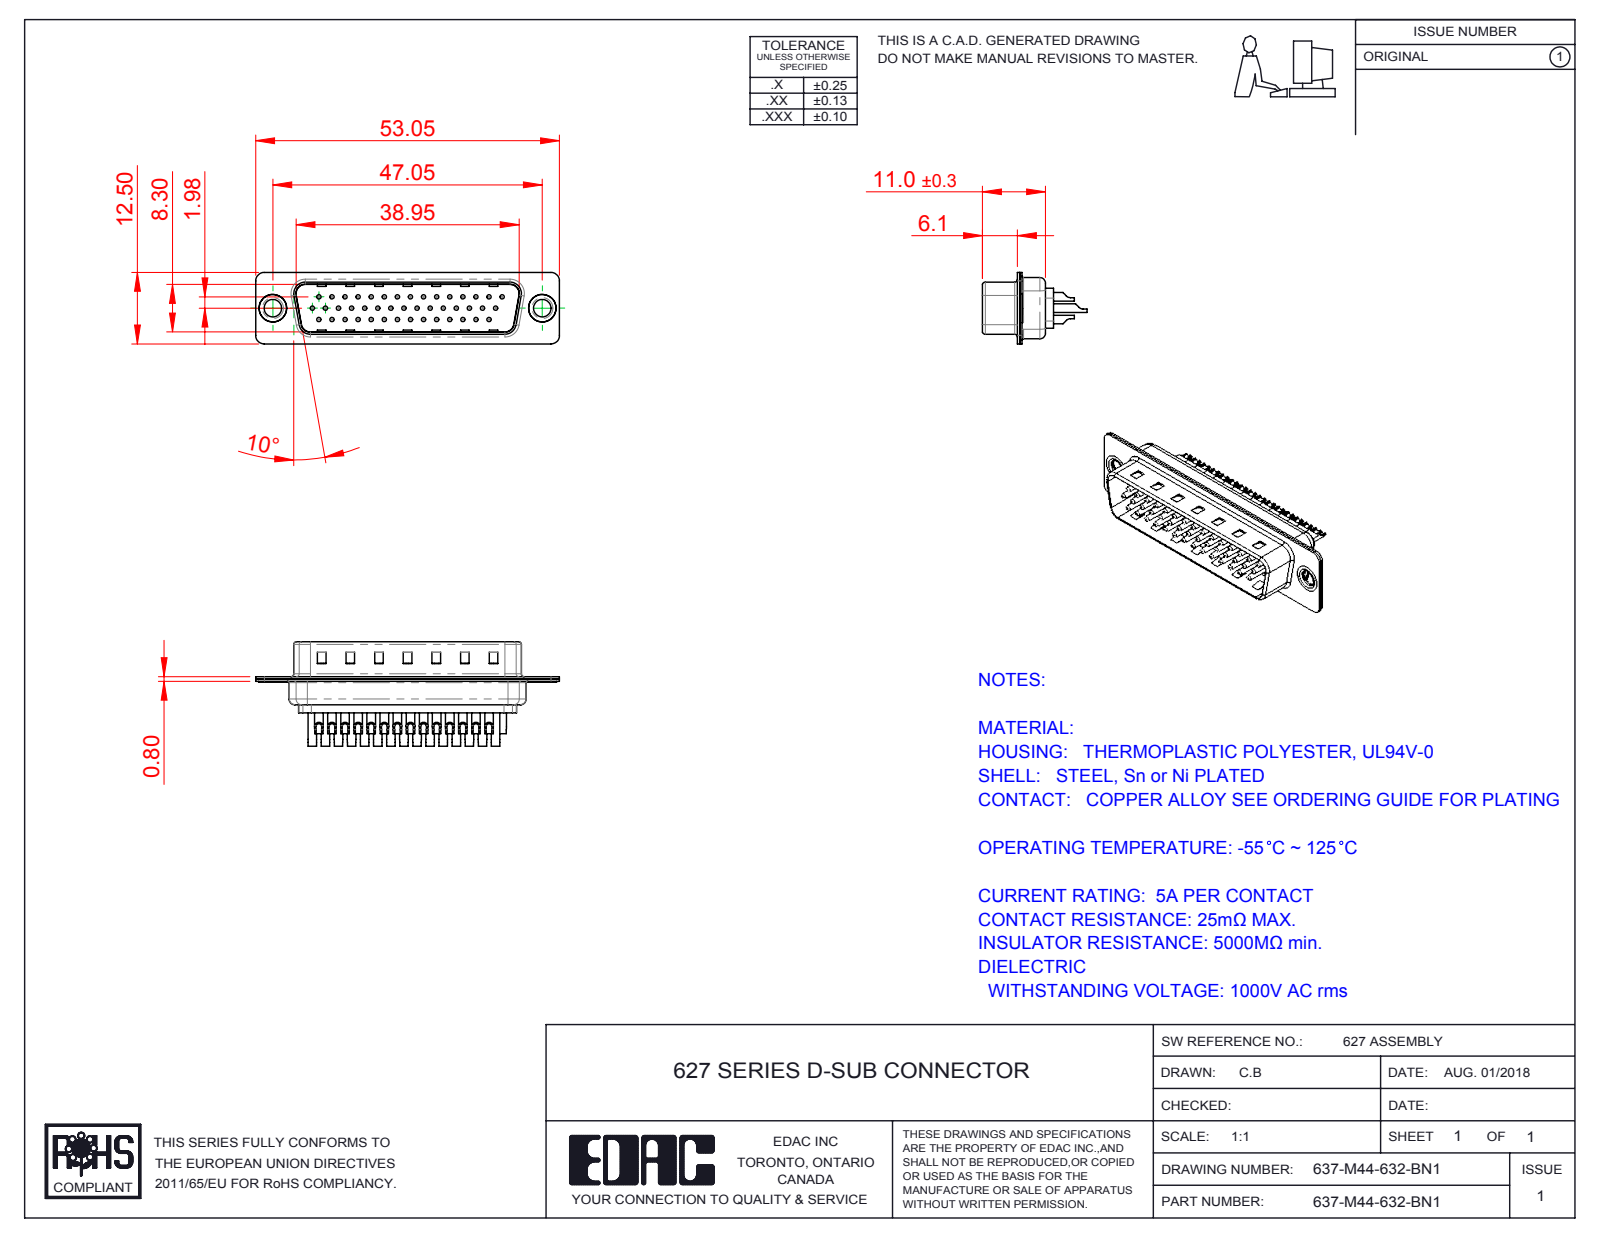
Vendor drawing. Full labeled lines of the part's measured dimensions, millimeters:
Part name (STEP PRODUCT): 637M Contact Row 3_32; 637M Housing_44 Contacts; 637M Contact Row 2_32; 637M Shell Rear_44 Contacts (+4 more)
STEP written by: SolidWorks 2016 (CONFIG_CONTROL_DESIGN)
Units: millimetres
Bodies: 49 solids, 1978 faces (567 planar, 825 cylindrical, 586 other)
Overall size (bounding box): 53.05 × 18.25 × 12.5
Volume: 2 896 mm³ · Surface area: 8 864 mm²
Round holes (diameter × count): ⌀0.75 ×44, ⌀1 ×44, ⌀1.6 ×44, ⌀2 ×44, ⌀3.05 ×2, ⌀4 ×2, ⌀4.8 ×2
Round bosses / shafts (diameter × count): ⌀1.5 ×44, ⌀2 ×3, ⌀0.75 ×3, ⌀5 ×2, ⌀4.9 ×2, ⌀3.55 ×2
Partial cylindrical surfaces — rounded edges, fillets, slot ends (radius × count): R1.5 ×16, R2 ×12, R0.5 ×8, R1.6 ×8, R1 ×7, R0.25 ×4, R0.6 ×4, R0.65 ×4
Main face-to-face distances: 0.4, 0.8, 9.5, 9.1, 8.7, 9.9, 0.75, 1.1, 0.35, 1.2
Hole centre spacings: 2.28, 3.96, 2.29, 4.57, 8.24, 6.86, 11.43, 14.99
